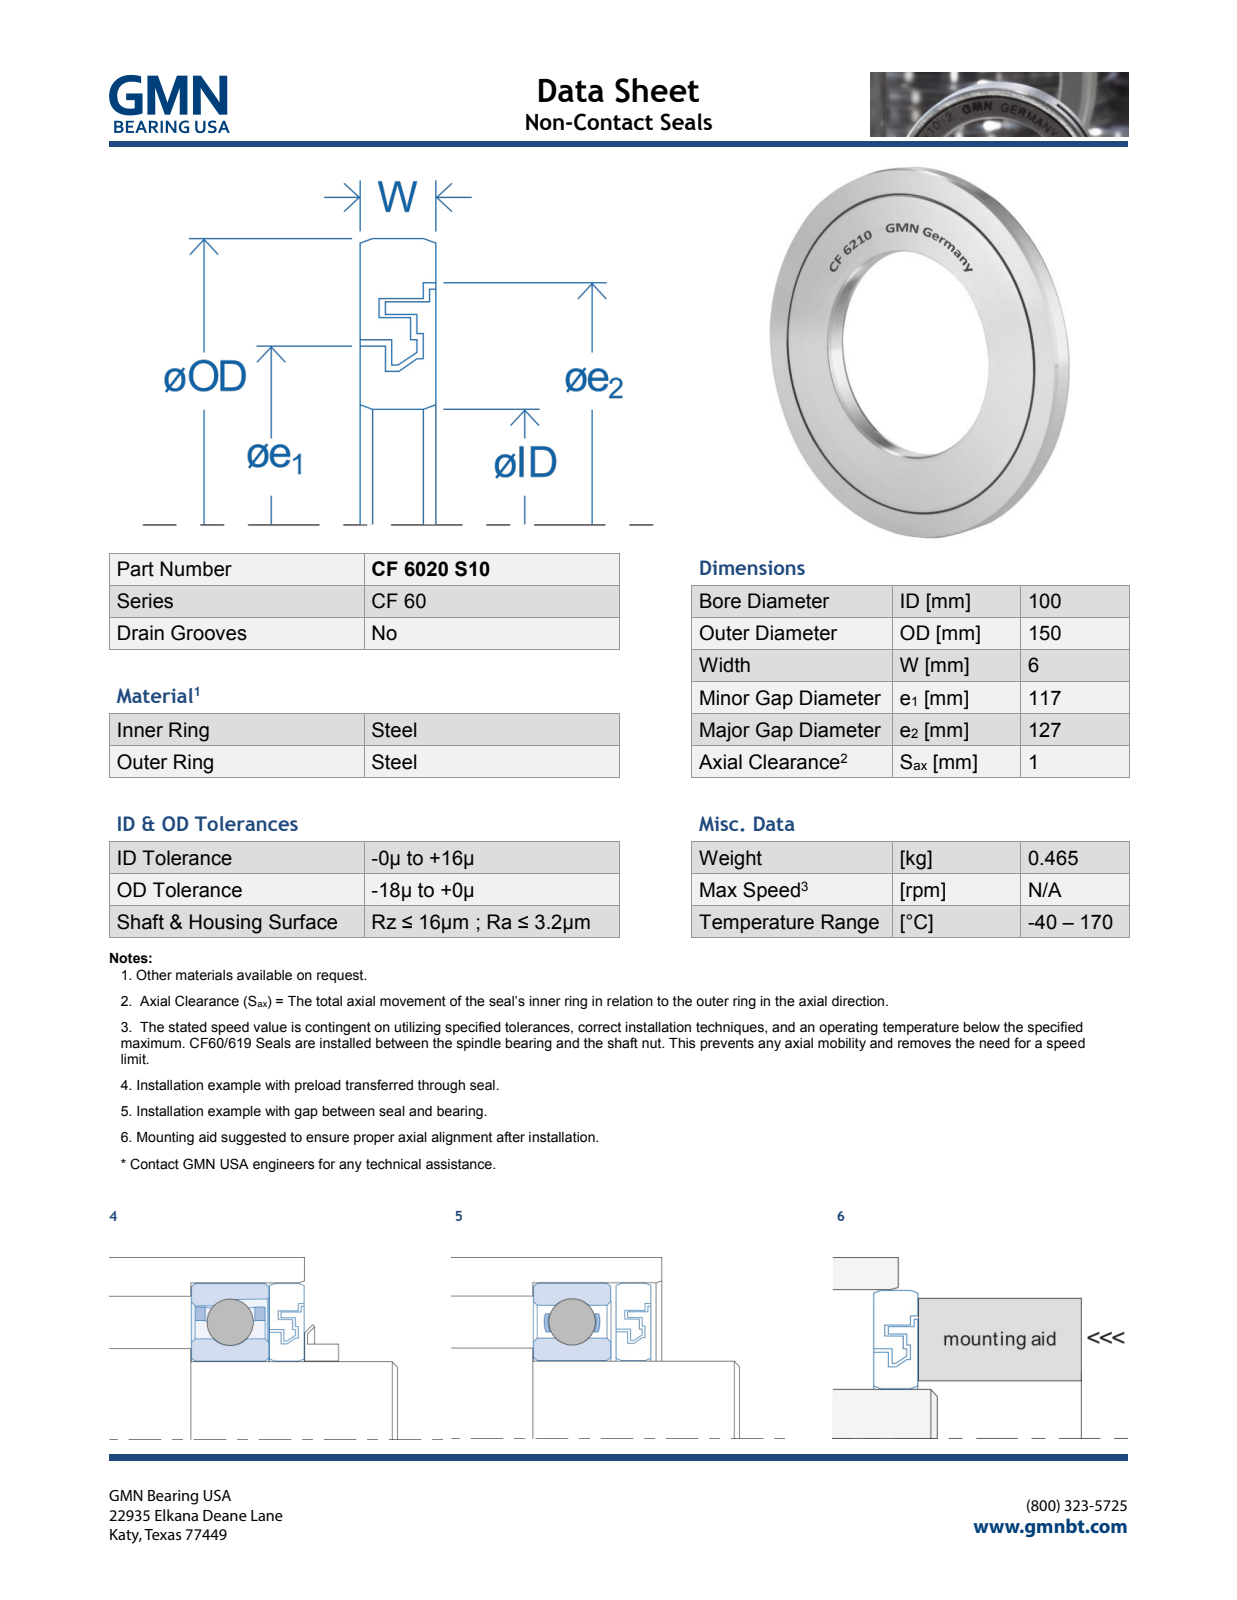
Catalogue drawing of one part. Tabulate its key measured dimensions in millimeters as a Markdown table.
| quantity | value |
| --- | --- |
| part name | CF6020S10_PRT |
| STEP written by | PRO/ENGINEER BY PARAMETRIC TECHNOLOGY CORPORATION, 2013150 (AUTOMOTIVE_DESIGN) |
| units | millimeters |
| bodies | 2 solids, 674 faces (632 planar, 30 cylindrical, 12 other) |
| overall size | 150 × 150 × 6.05 |
| volume | 55 525 mm³ |
| surface area | 38 425 mm² |
| round holes (diameter × count) | 100 × 1, 114 × 1, 118 × 1, 119 × 1, 122 × 1, 124.5 × 1, 127 × 1 |
| round bosses / shafts (diameter × count) | 150 × 1, 126 × 1, 124 × 1, 121.5 × 1, 117 × 1, 115 × 1, 113 × 1 |
| main face-to-face distances | 6, 0.5, 2, 2.5, 1, 1.5, 4, 3, 3.5, 4.5 |
